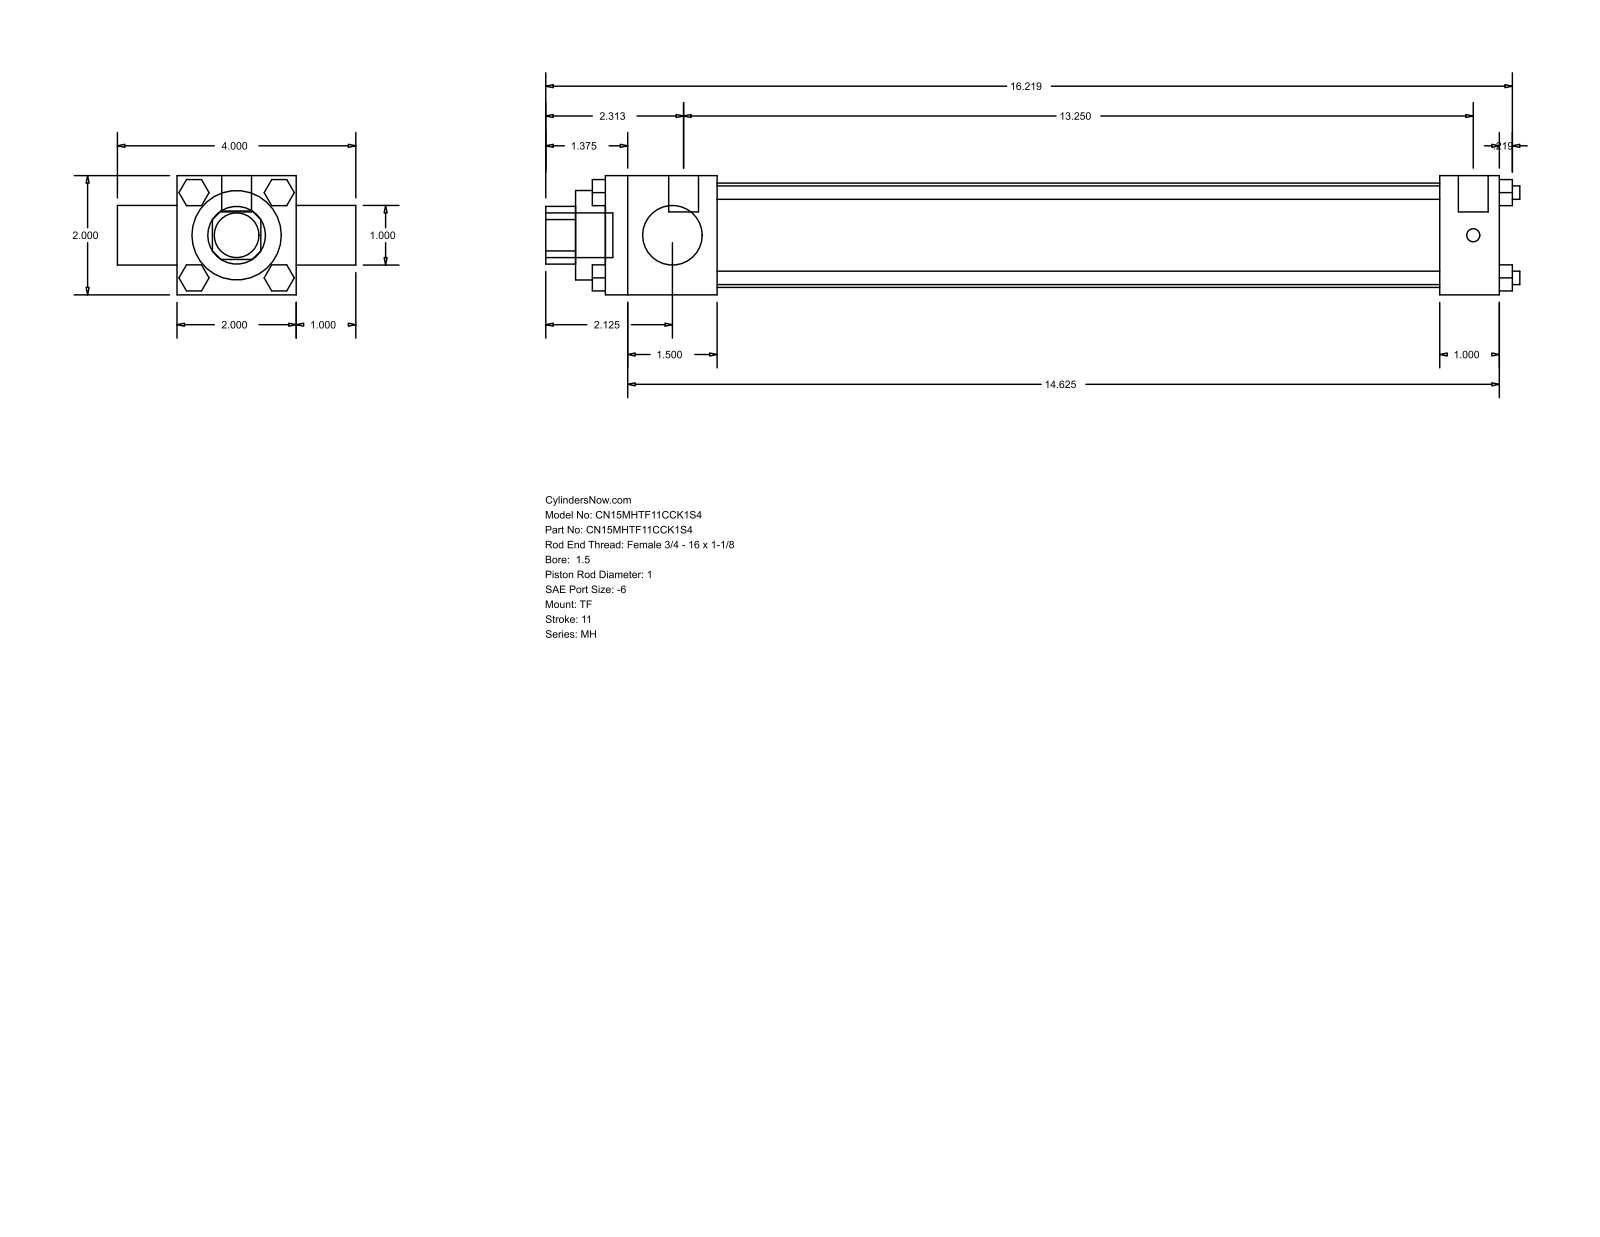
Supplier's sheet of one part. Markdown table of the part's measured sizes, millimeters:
| quantity | value |
| --- | --- |
| part name | MH_TF__0150_1 |
| STEP written by | GSSL Pune (CONFIG_CONTROL_DESIGN) |
| units | millimeters |
| bodies | 0 solids, 120 faces (92 planar, 28 cylindrical, 0 other) |
| overall size | 415.13 × 101.6 × 50.8 |
| round holes (diameter × count) | 25.4 × 2, 38.1 × 1, 44.45 × 1 |
| round bosses / shafts (diameter × count) | 5.71 × 4, 5.56 × 3, 12.7 × 2, 19.05 × 1 |
| partial cylindrical surfaces (radius × count) | 12.29 × 1 |
| main face-to-face distances | 50.8, 25.4, 381, 76.2, 47.63, 333.37, 355.6, 307.97, 386.56, 12.7 |
